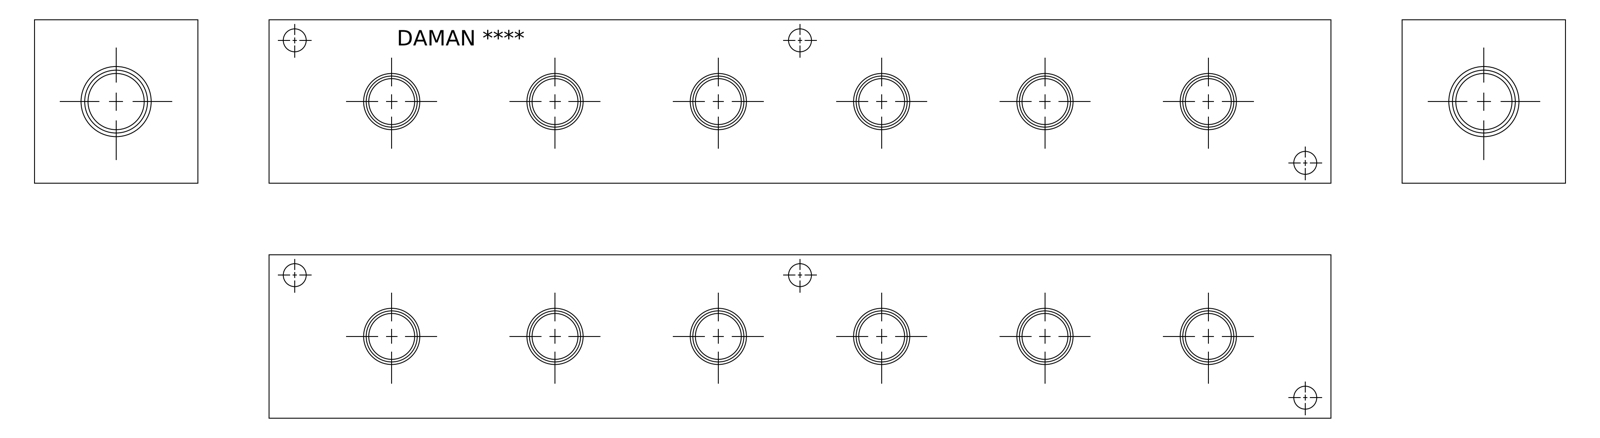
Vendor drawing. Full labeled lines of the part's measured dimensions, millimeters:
Part name (STEP PRODUCT): Part_AH0900606P_3D
STEP written by: Autodesk Inventor 2019 (AUTOMOTIVE_DESIGN)
Units: millimetres
Bodies: 1 solid, 392 faces (217 planar, 40 cylindrical, 135 other)
Overall size (bounding box): 330.2 × 50.8 × 50.8
Volume: 791 703 mm³ · Surface area: 88 822 mm²
Round holes (diameter × count): ⌀14.3 ×12, ⌀17.3 ×12, ⌀7.14 ×6, ⌀17.48 ×1, ⌀21.59 ×1
Main face-to-face distances: 50.8, 330.2, 11.73, 39.07, 15.37, 314.83, 299.46, 49.8, 10.73, 1
Hole centre spacings: 50.8, 101.6, 152.4, 31.75, 35.69, 78.55, 83.19, 128.42
